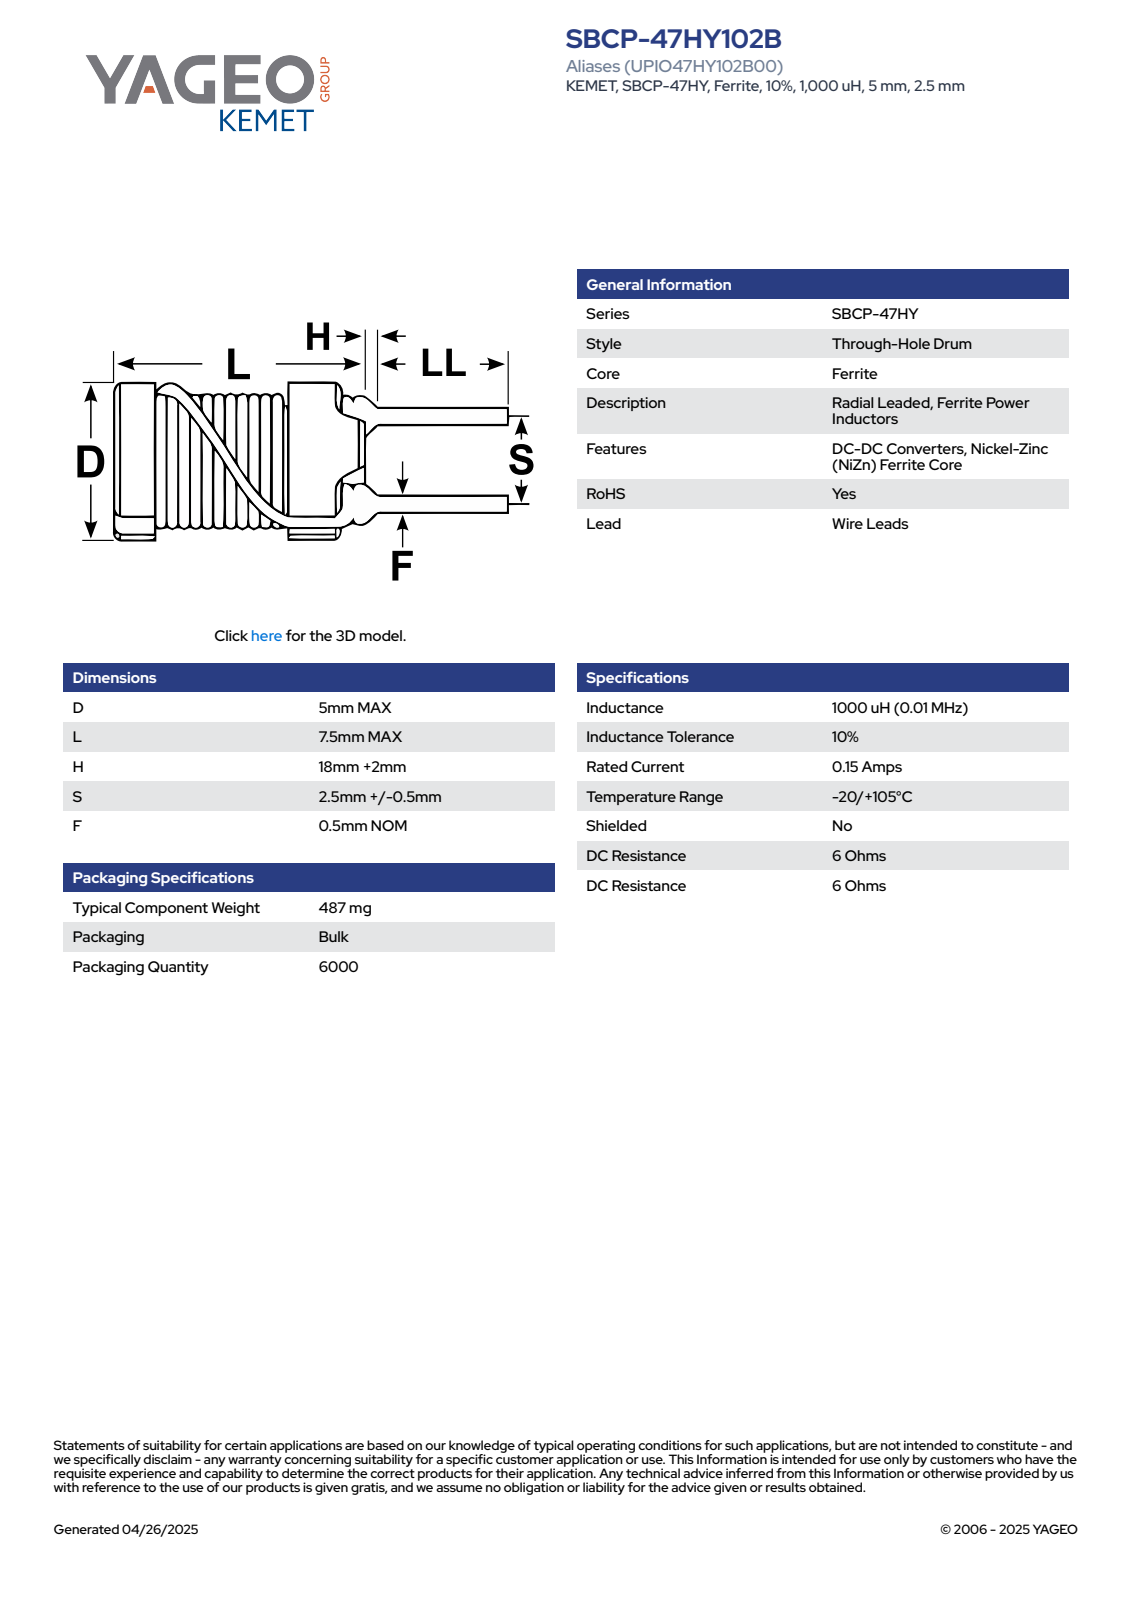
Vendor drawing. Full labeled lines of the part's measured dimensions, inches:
Part name (STEP PRODUCT): IL_SBCP47_D5L7.5S2.5LL4F0.5
STEP written by: SolidWorks 2014 (AUTOMOTIVE_DESIGN)
Units: inches
Bodies: 4 solids, 101 faces (70 planar, 17 cylindrical, 14 other)
Overall size (bounding box): 0.453 × 0.197 × 0.197
Volume: 0.007 in³ · Surface area: 0.271 in²
Round holes (diameter × count): ⌀0.165 ×1
Round bosses / shafts (diameter × count): ⌀0.035 ×2, ⌀0.02 ×2, ⌀0.197 ×1
Main face-to-face distances: 0.26, 0.049, 0.223, 0.037, 0.174, 0.211, 0.035, 0.085, 0.258, 0.295
